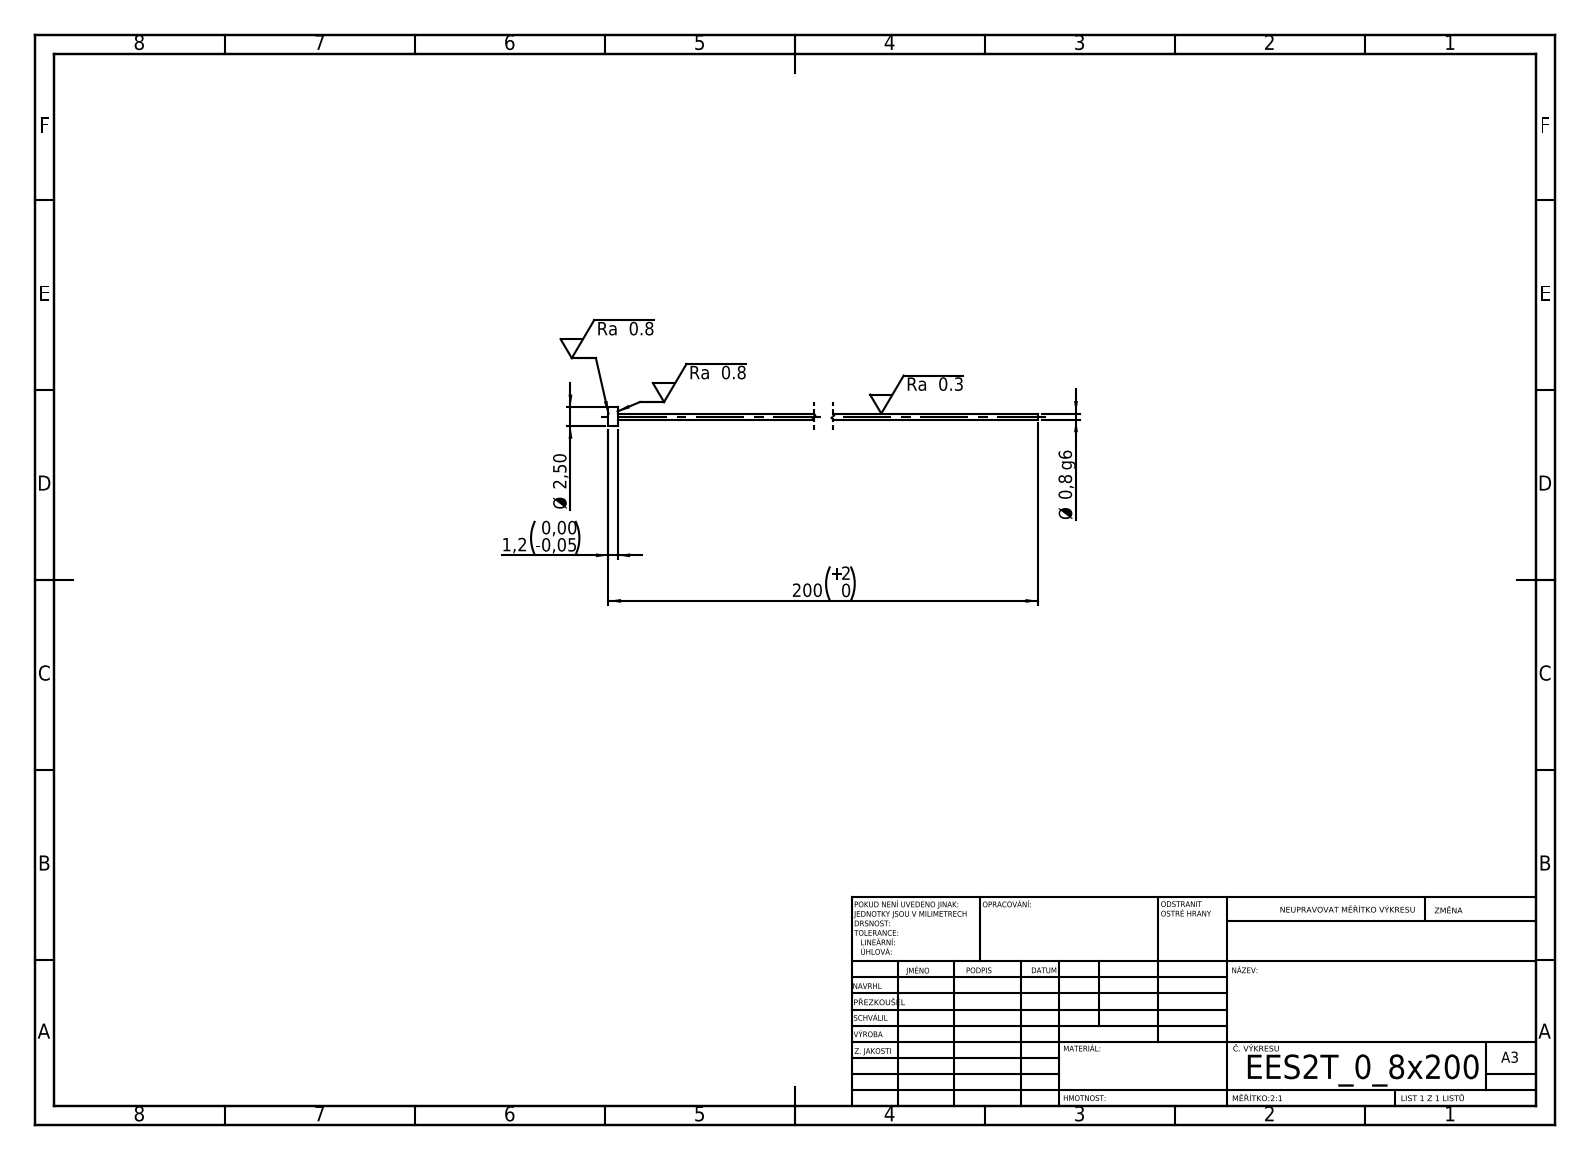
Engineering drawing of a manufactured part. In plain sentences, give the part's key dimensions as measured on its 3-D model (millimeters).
Its 3-D file was written by "SolidWorks 2019 (CONFIG_CONTROL_DESIGN)". It is 1 solid with 7 faces: 3 planar, 4 cylindrical and 0 other. Overall it measures 200 by 2.5 by 2.5 millimeters. Its volume is 106 cubic millimeters and its surface area 519 square millimeters. Round bosses or shafts: 1 of diameter 2.5, 1 of diameter 0.8. The main face-to-face distances are 1.2, 200, 198.8.
